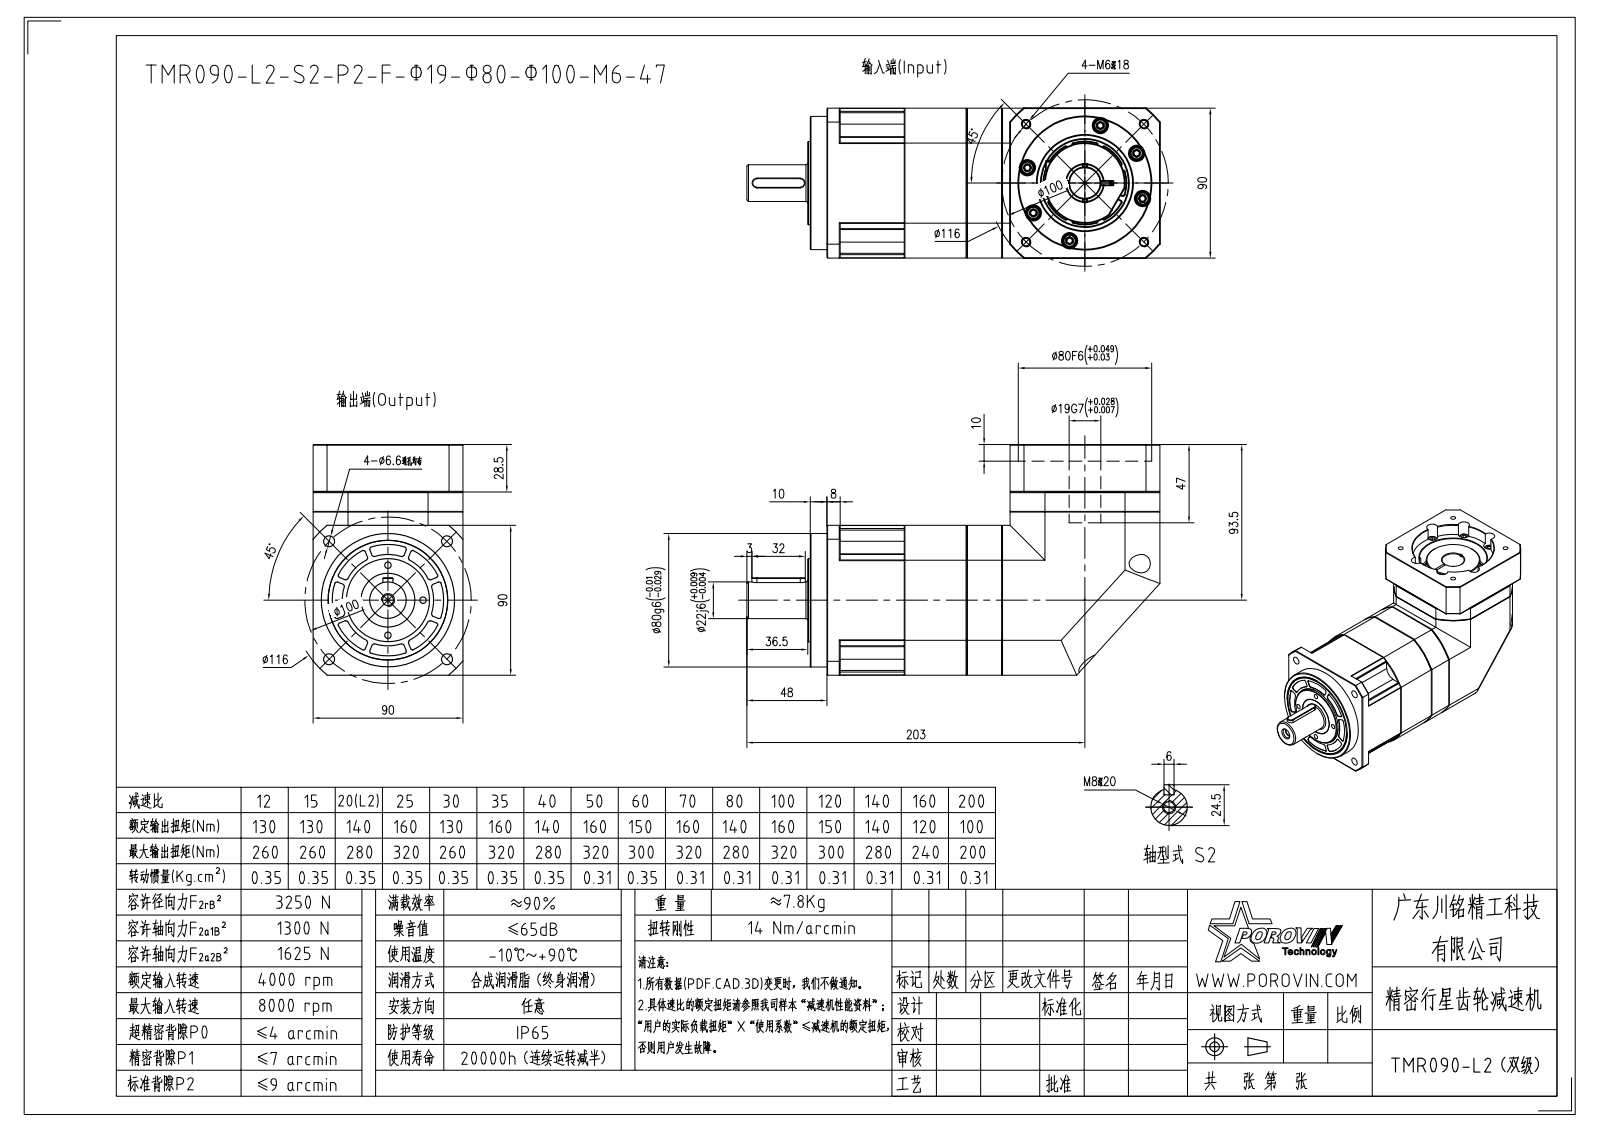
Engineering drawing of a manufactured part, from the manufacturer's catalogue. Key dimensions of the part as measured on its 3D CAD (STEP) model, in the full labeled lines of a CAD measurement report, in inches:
Part name (STEP PRODUCT): HEXAGON_SOCKET_HEAD_CAP_SCR-935; HEX_SOCKET_SET_SCREWS_WITH_FLAT; SPRING_LOCK_WASHERS--NORM-20979; SPRING_LOCK_WASHERS--NORMAL-834 (+8 more)
STEP written by: CREO PARAMETRIC BY PTC INC, 2020053 (CONFIG_CONTROL_DESIGN)
Units: inches
Bodies: 43 solids, 1321 faces (526 planar, 561 cylindrical, 234 other)
Overall size (bounding box): 9.764 × 5.453 × 3.543
Volume: 97.7 in³ · Surface area: 369.9 in²
Round holes (diameter × count): ⌀0.213 ×12, ⌀0.217 ×12, ⌀0.374 ×12, ⌀0.26 ×10, ⌀0.165 ×7, ⌀0.197 ×5, ⌀0.256 ×5, ⌀0.157 ×4, ⌀0.263 ×4, ⌀0.433 ×4, ⌀0.268 ×1, ⌀0.331 ×1
Round bosses / shafts (diameter × count): ⌀0.335 ×12, ⌀0.315 ×12, ⌀0.197 ×12, ⌀0.394 ×4, ⌀0.389 ×4, ⌀0.236 ×4, ⌀3.15 ×1, ⌀3.071 ×1
Partial cylindrical surfaces — rounded edges, fillets, slot ends (radius × count): R0.039 ×92, R0.295 ×4, R2.008 ×3, R0.118 ×2, R2.283 ×2, R0.157 ×1, R0.207 ×1, R0.817 ×1
Main face-to-face distances: 3.543, 0.472, 0.846, 0.839, 1.476, 2.315, 2.323, 4.331, 0.394, 3.858
Hole centre spacings: 1.407, 1.077, 1.502, 1.732, 1.969, 2.601, 2.619, 2.784
